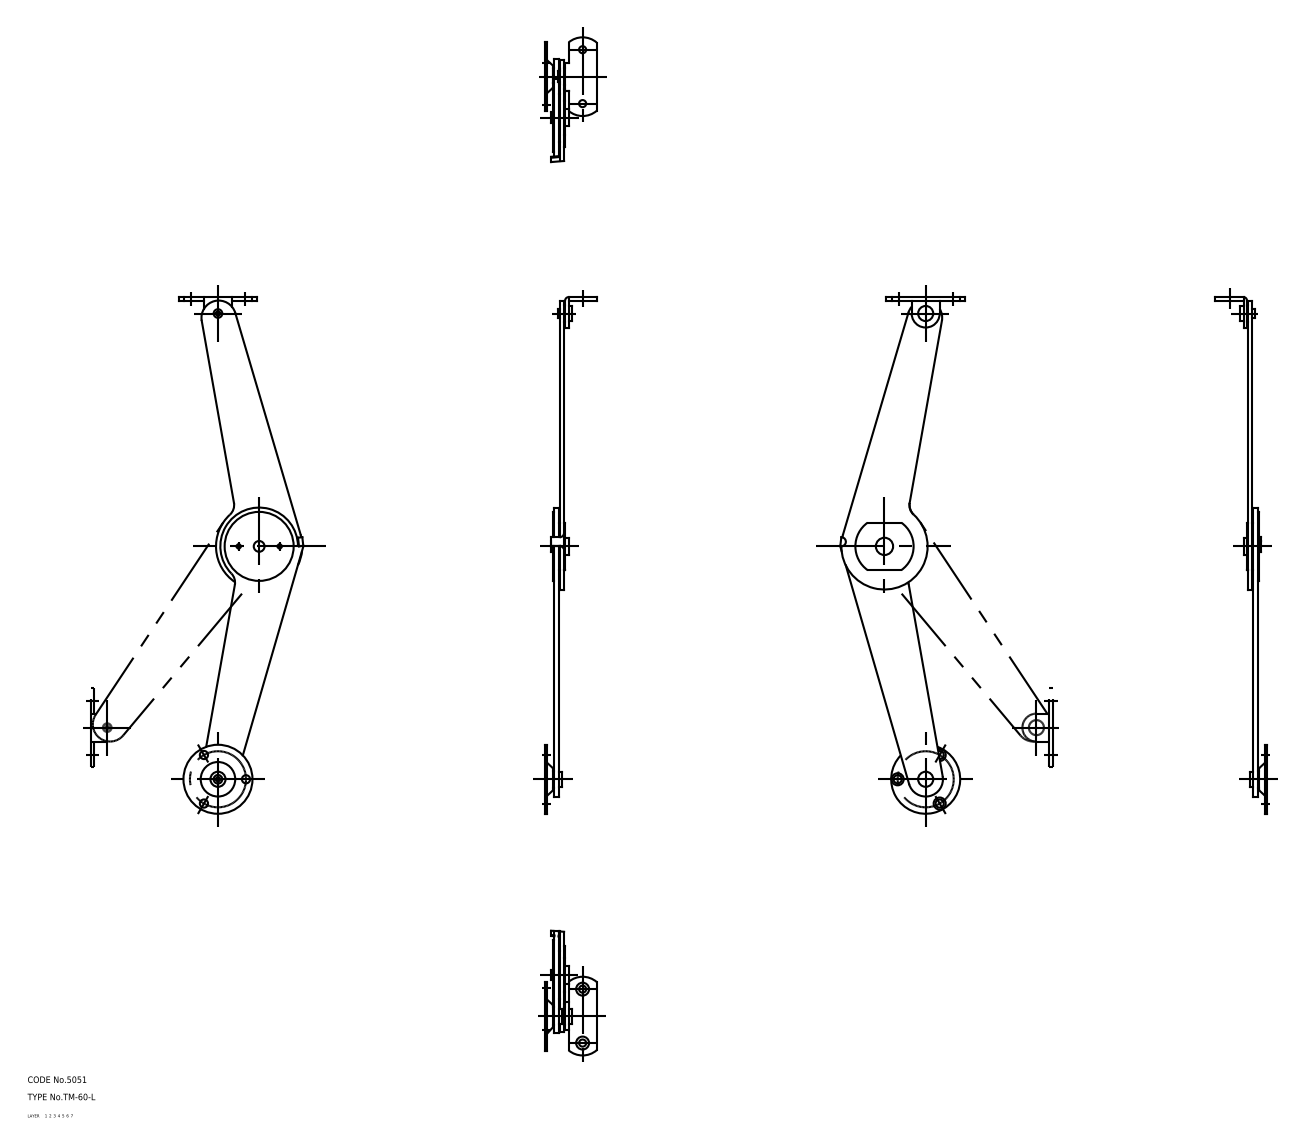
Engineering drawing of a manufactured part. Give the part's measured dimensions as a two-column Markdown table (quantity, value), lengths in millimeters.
| quantity | value |
| --- | --- |
| part name | ball; washer_A; washer_B; spring_A (+8 more) |
| STEP written by | CADfix (AUTOMOTIVE_DESIGN) |
| units | millimeters |
| bodies | 13 solids, 156 faces (0 planar, 0 cylindrical, 156 other) |
| overall size | 239.6 × 57.85 × 24 |
| volume | 16 003 mm³ |
| surface area | 20 597 mm² |
